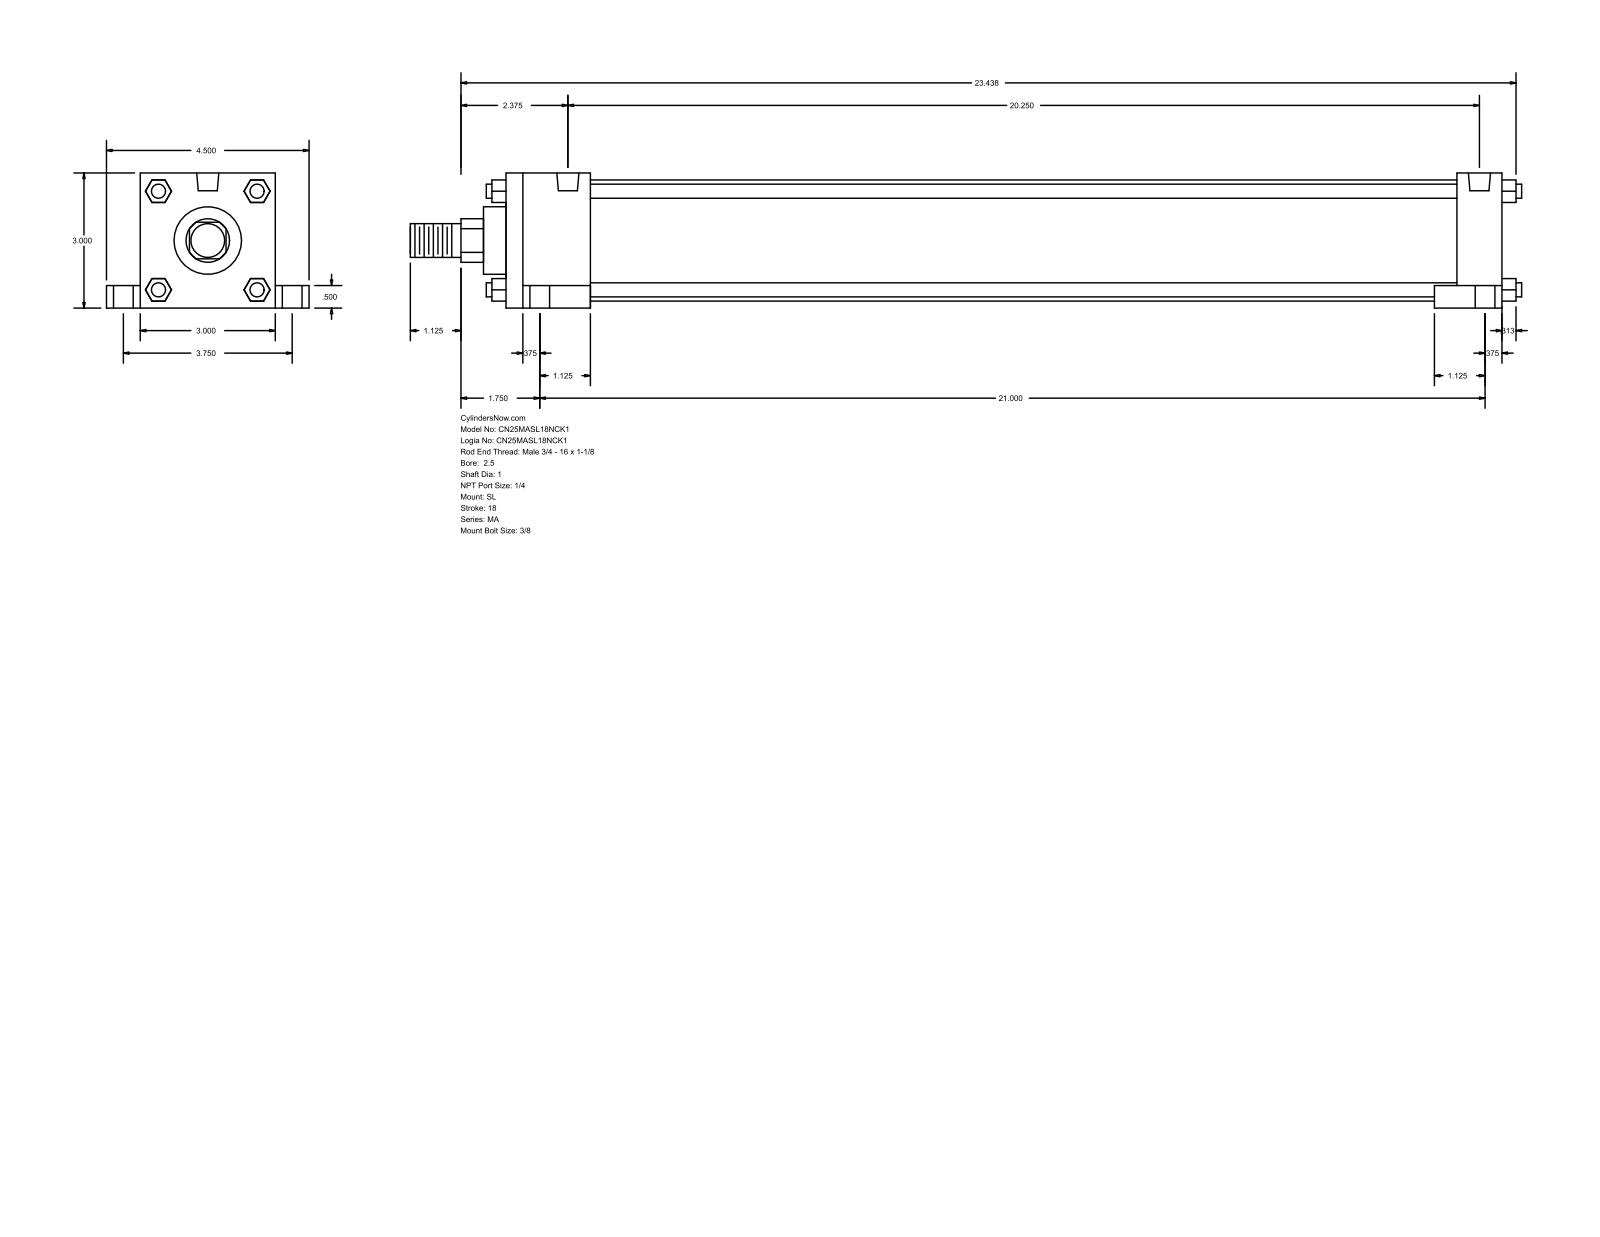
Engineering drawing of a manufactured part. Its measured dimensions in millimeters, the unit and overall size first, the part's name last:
Units: millimetres
Overall size (bounding box): 627.06 × 114.3 × 76.2
Round holes (diameter × count): ⌀7.94 ×4, ⌀11.11 ×4, ⌀17.46 ×4, ⌀12.49 ×2
Round bosses / shafts (diameter × count): ⌀7.94 ×4, ⌀68.33 ×1, ⌀38.1 ×1, ⌀25.4 ×1, ⌀19.05 ×1
Partial cylindrical surfaces — rounded edges, fillets, slot ends (radius × count): R12.29 ×1
Main face-to-face distances: 76.2, 561.98, 12.7, 488.95, 25.4, 47.63, 514.35, 536.58, 19.05, 95.25
Hole centre spacings: 47.73, 50.2, 95.24, 514.34, 519.71, 532.35, 533.4, 541.84
Bodies: 0 solids, 148 faces (112 planar, 36 cylindrical, 0 other)
Part name (STEP PRODUCT): MA_SL__0250_1
STEP written by: GSSL Pune (CONFIG_CONTROL_DESIGN)
